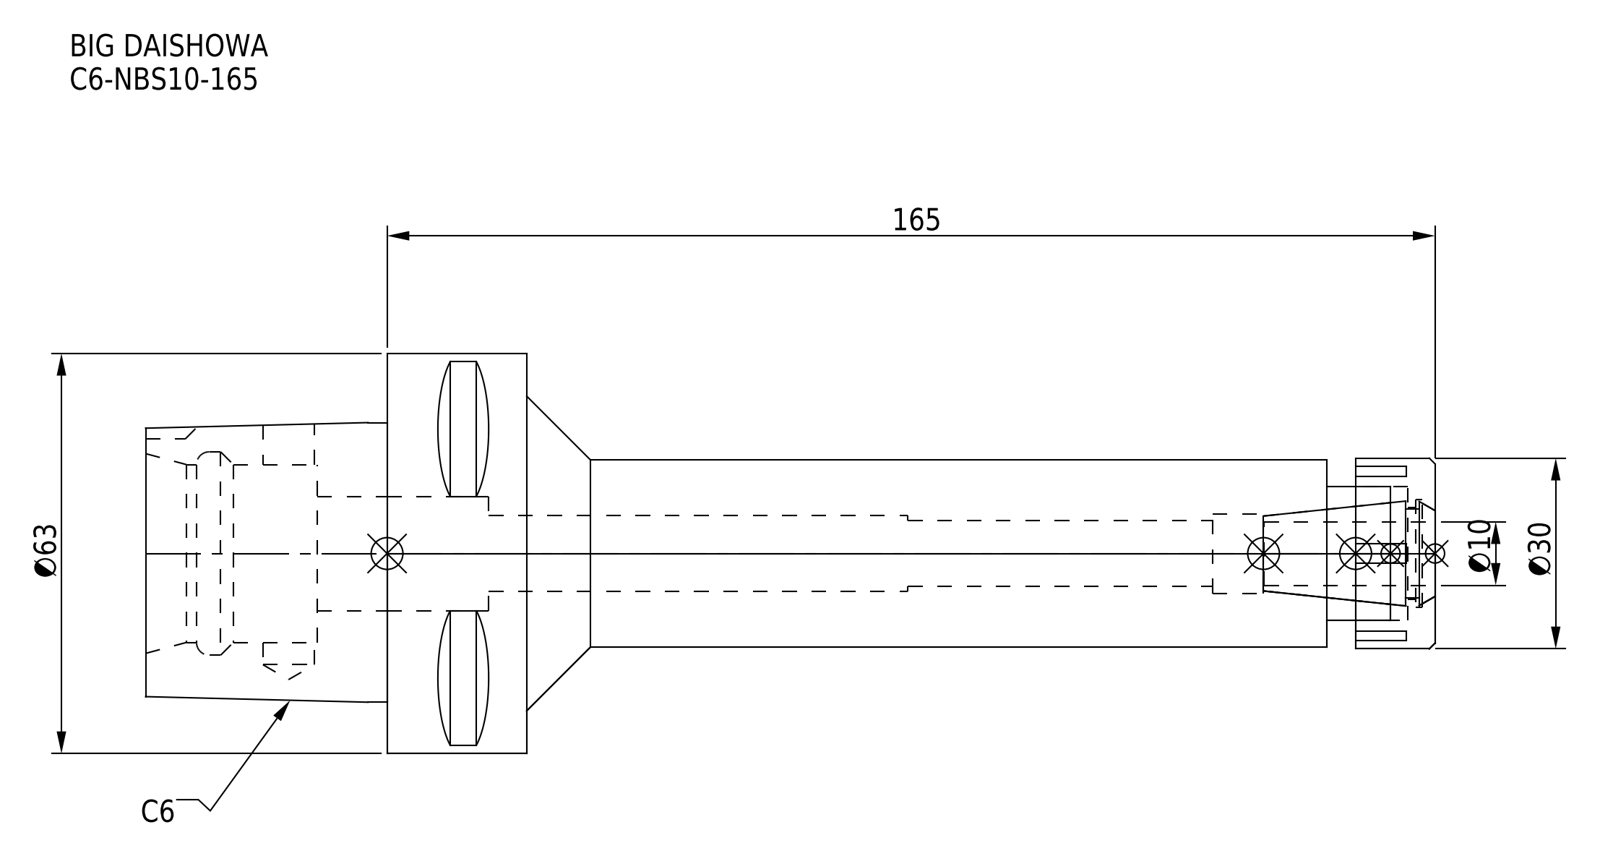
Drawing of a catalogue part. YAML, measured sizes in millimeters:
part_name: "C6-NBS10-165-100_ASM.stp; C6-NBS10-165-FreeParts; C6-NBS10-165_1.stp; NBN10_1.stp (+3 more)"
step_written_by: "SolidWorks 2019 (CONFIG_CONTROL_DESIGN)"
units: millimeters
bodies: {solids: 2, faces: 112, planar: 61, cylindrical: 33, other: 18}
overall_size: [203, 63, 63]
volume: 181163
surface_area: 40349
round_holes:
  - {diameter: 8.1, count: 1}
  - {diameter: 10.4, count: 1}
  - {diameter: 12, count: 1}
  - {diameter: 12.5, count: 1}
  - {diameter: 14.5, count: 1}
  - {diameter: 17, count: 1}
  - {diameter: 18, count: 1}
  - {diameter: 21, count: 1}
  - {diameter: 28, count: 1}
  - {diameter: 32, count: 1}
round_bosses_or_shafts:
  - {diameter: 63, count: 1}
  - {diameter: 30, count: 1}
  - {diameter: 29.5, count: 1}
partial_cylinders:
  - {radius: 5, count: 1}
face_to_face_distances: [22, 60, 27, 38, 143, 165, 203, 33, 176, 11]
